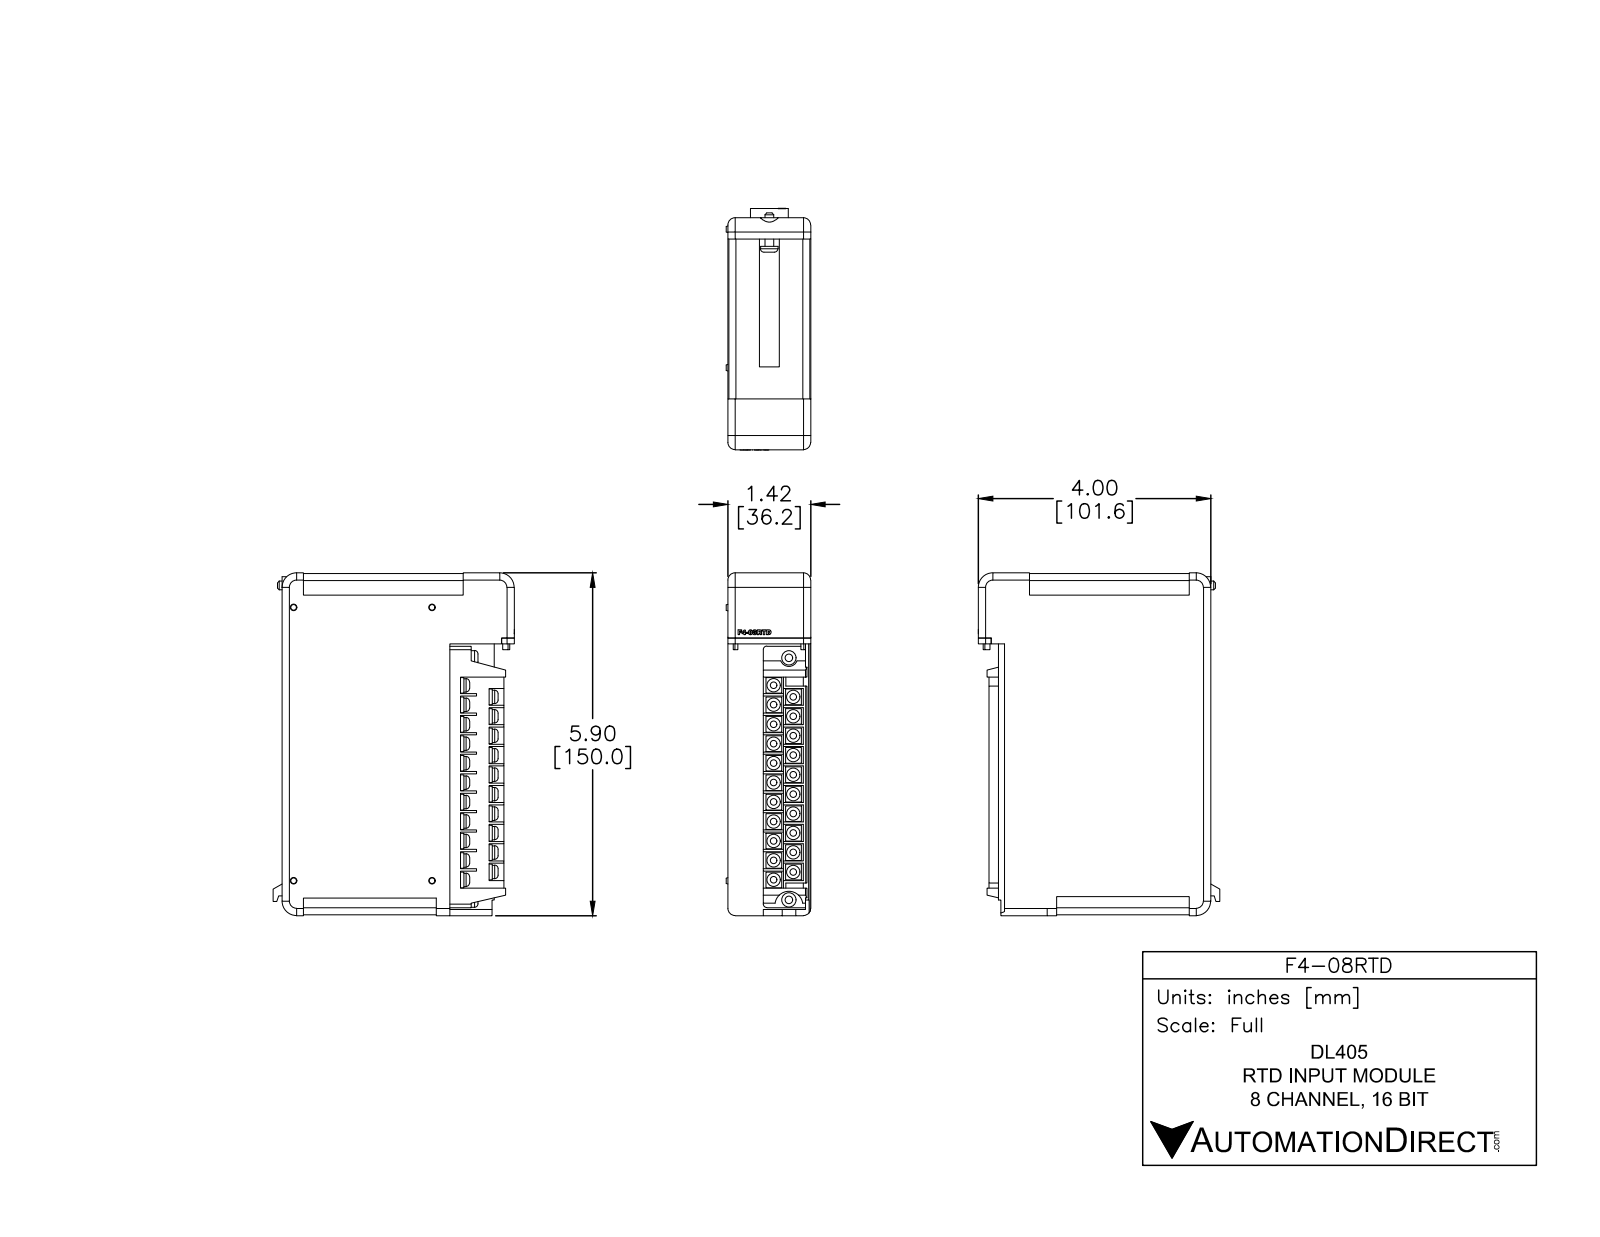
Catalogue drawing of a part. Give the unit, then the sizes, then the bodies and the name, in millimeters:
Units: millimetres
Overall size (bounding box): 150 × 105.6 × 37
Round bosses / shafts (diameter × count): ⌀5.8 ×21, ⌀6.4 ×2, ⌀7.6 ×1, ⌀3.8 ×1
Partial cylindrical surfaces — rounded edges, fillets, slot ends (radius × count): R3.2 ×8, R3 ×4, R6.4 ×3, R0.4 ×2, R0.8 ×2, R1.5 ×2, R3.8 ×1, R3.8 ×1
Main face-to-face distances: 36.2, 0.4, 73.4, 149.2, 35.8, 11.9, 5.1, 24.3, 149.6, 30.7
Volume: 450 800 mm³ · Surface area: 56 020 mm²
Bodies: 14 solids, 605 faces (416 planar, 86 cylindrical, 103 other)
Part name (STEP PRODUCT): F4-08RTD
STEP written by: SolidWorks 2014 (AUTOMOTIVE_DESIGN)
